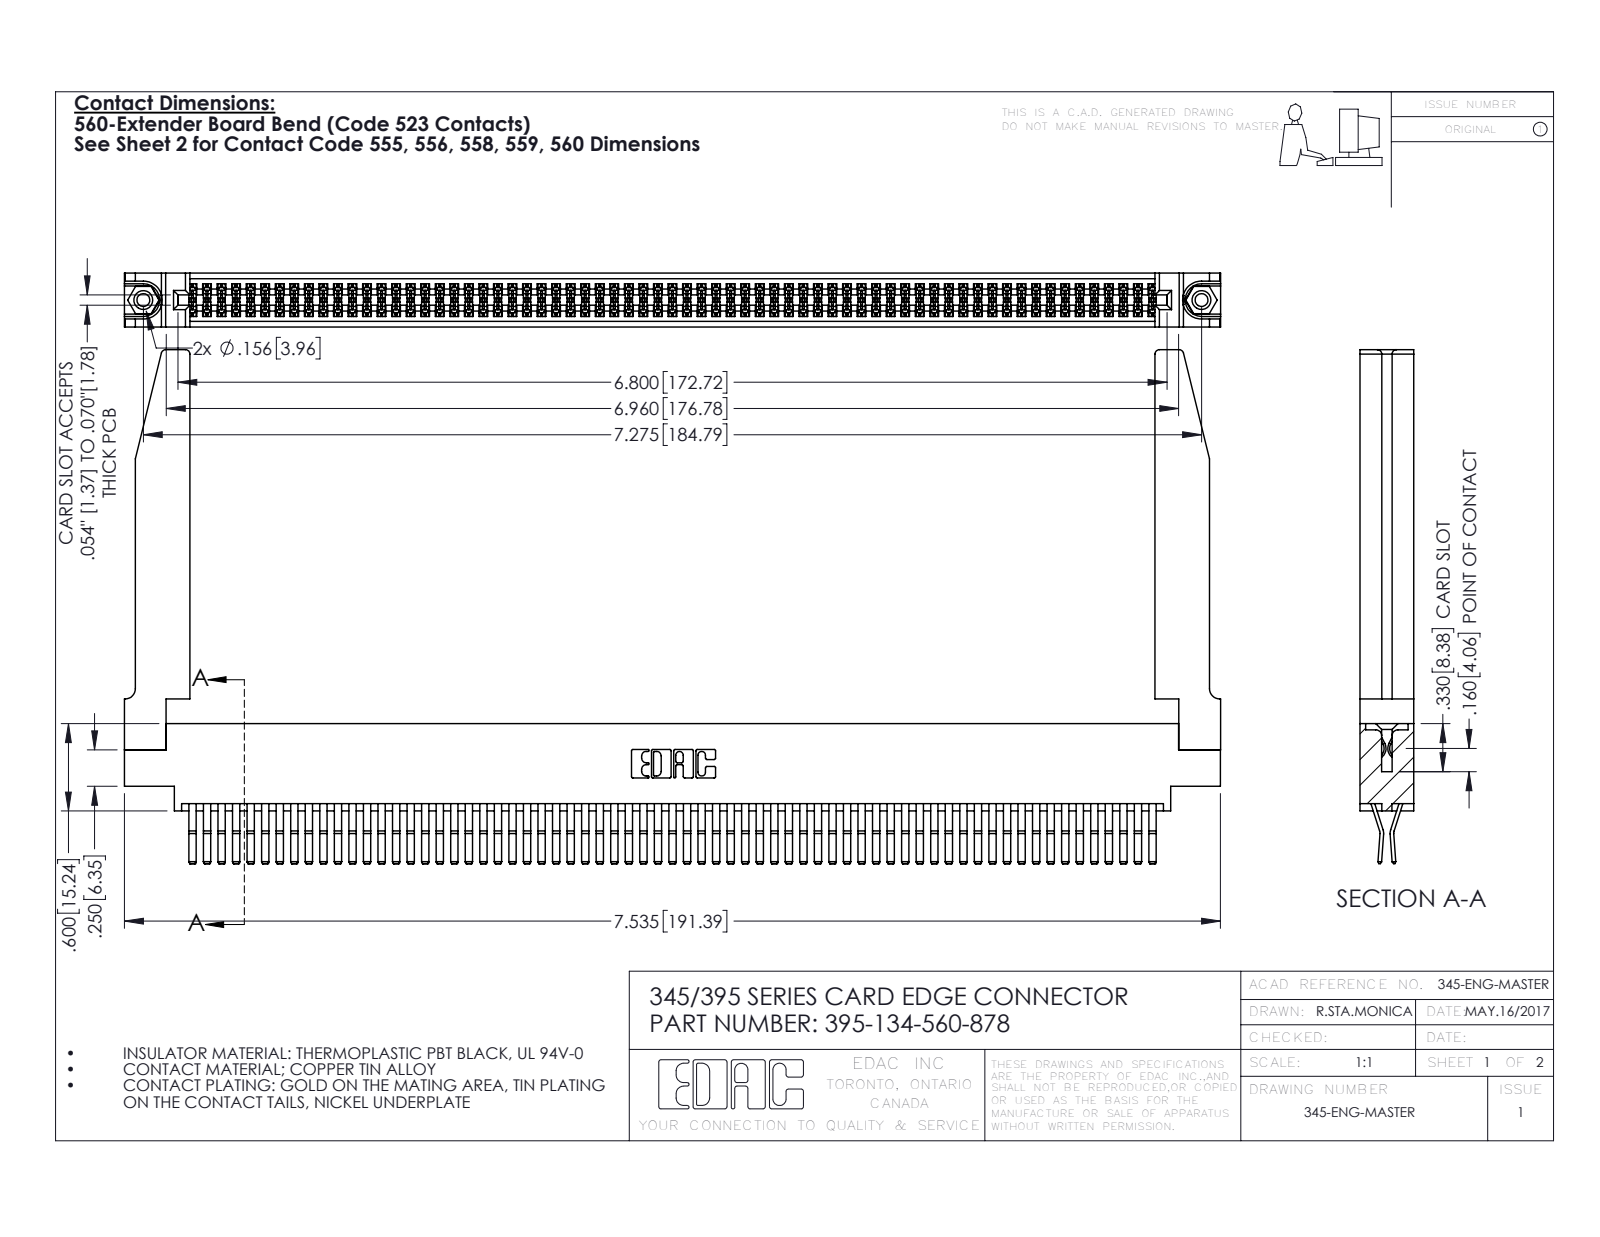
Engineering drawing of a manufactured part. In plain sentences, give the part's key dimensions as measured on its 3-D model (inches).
The part is named "345-292-001_560 Tail; 395-134-560-878; 345 Part_0.170 Offset - 0.156 Dia-TH; 345-250-001_345-250-001-102 (+1 more)". Its 3-D file was written by "SolidWorks 2016 (CONFIG_CONTROL_DESIGN)". It is 139 solids with 7332 faces: 4648 planar, 2632 cylindrical and 52 other. Overall it measures 7.536 by 3.532 by 0.37 inches. Its volume is 1.67 cubic inches and its surface area 59.96 square inches. Round holes: 2 of diameter 0.089, 2 of diameter 0.125, 2 of diameter 0.156, 1 of diameter 0.064. Round bosses or shafts: 2 of diameter 0.155. Partial cylindrical surfaces (rounded edges, fillets, slot ends): 201 of radius 0.006, 22 of radius 0.01, 8 of radius 0.03, 6 of radius 0.007, 6 of radius 0.031, 3 of radius 0.026, 2 of radius 0.01, 2 of radius 0.014. The main face-to-face distances are 0.072, 0.37, 0.025, 0.298, 0.098, 0.272, 0.2, 0.225, 0.175, 0.149. The hole center spacings are 0.27, 7.039, 7.275.
